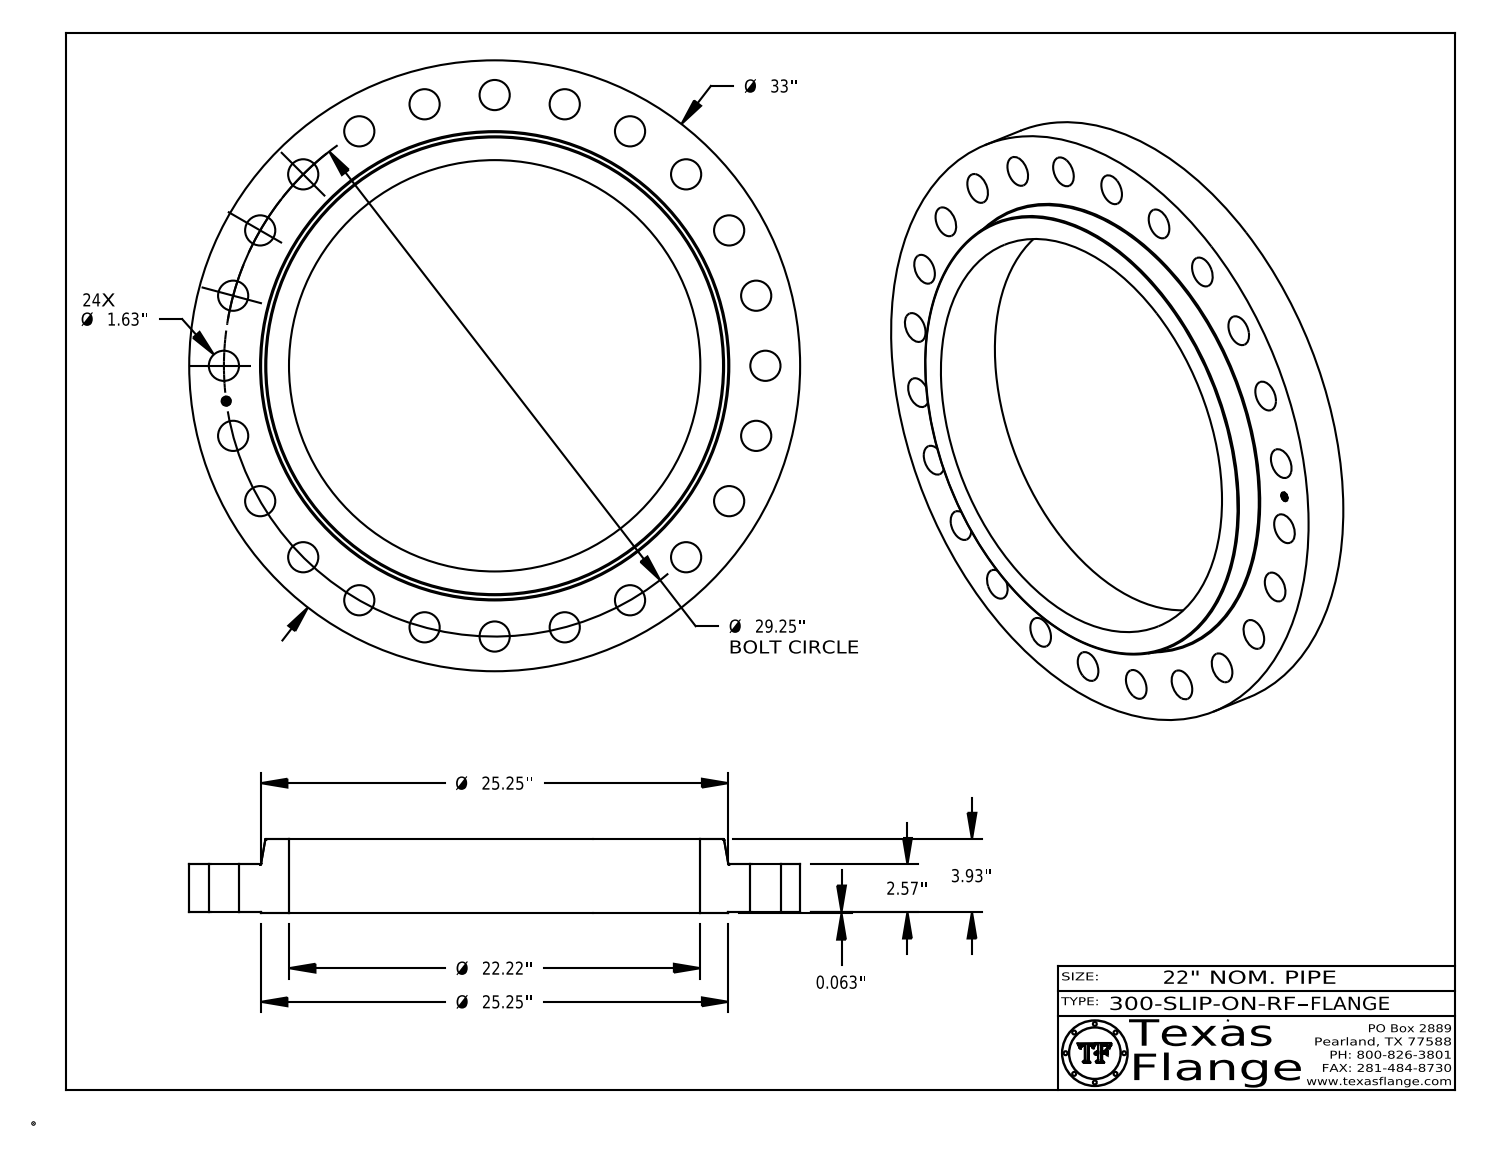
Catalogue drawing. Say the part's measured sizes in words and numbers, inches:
The part is named "300-SLIP-ON-RF". Its 3-D file was written by "CATIA V5 STEP AP214 (AUTOMOTIVE_DESIGN)". It is 1 solid with 449 faces: 369 planar, 74 cylindrical and 6 other. Overall it measures 33 by 33 by 3.993 inches. Its volume is 1 221 cubic inches and its surface area 1 788 square inches. Round holes: 24 of diameter 1.63, 1 of diameter 0.495, 1 of diameter 22.22. Round bosses or shafts: 8 of diameter 0.03, 1 of diameter 33, 1 of diameter 25.25, 1 of diameter 0.39. The main face-to-face distances are 2.57, 0.063, 2.633, 3.993, 3.93, 1.36, 2.618, 2.555, 0.015, 1.375. The hole center spacings are 14.625, 27.024, 7.57, 20.683, 3.818, 11.194, 17.806, 23.206.
